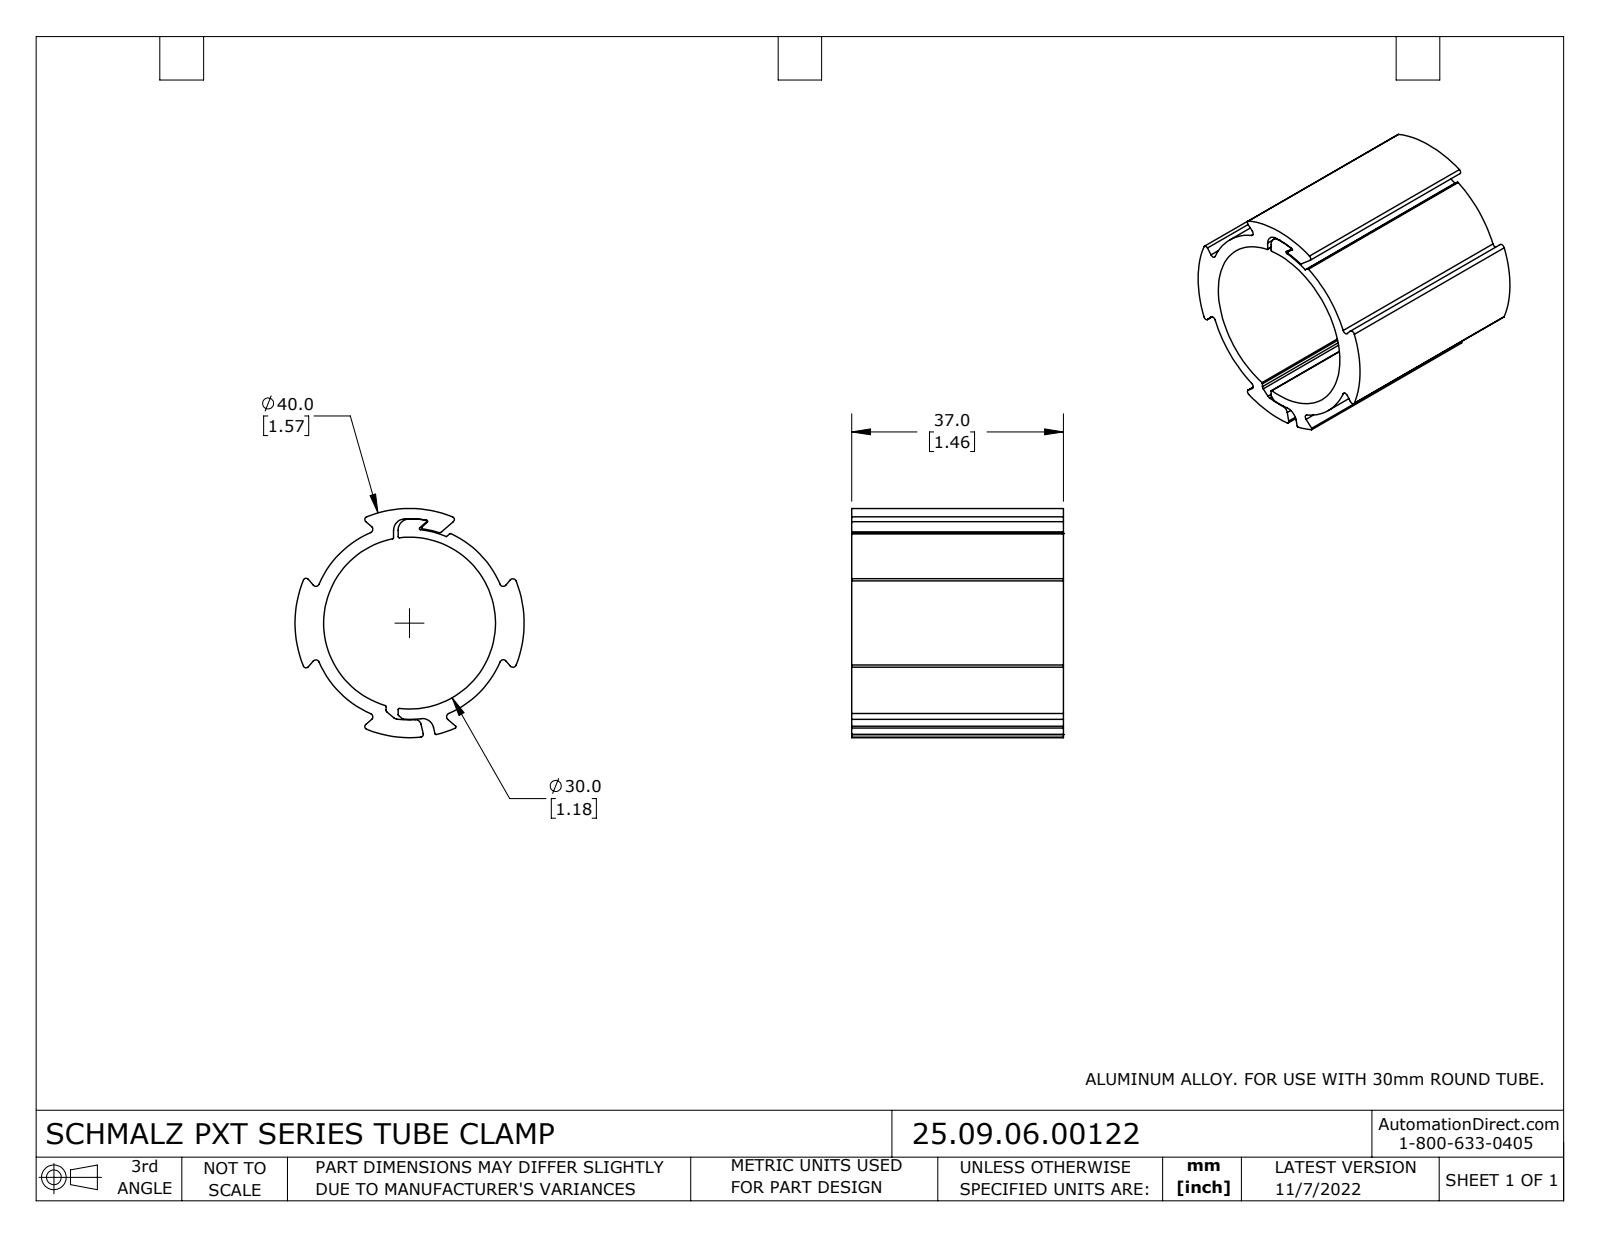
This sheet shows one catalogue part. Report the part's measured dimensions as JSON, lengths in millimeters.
{"part_name": "25.09.06.00122", "step_written_by": "SolidWorks 2021 (CONFIG_CONTROL_DESIGN)", "units": "millimeters", "bodies": {"solids": 2, "faces": 75, "planar": 23, "cylindrical": 52, "other": 0}, "overall_size": [40, 40, 37], "volume_mm3": 13716, "surface_area_mm2": 11109, "round_holes": [[30, 1]], "partial_cylinders_radius": [[0.2, 13], [0.6, 9], [0.5, 8], [2, 3], [1, 2], [16.4, 1], [16.6, 1], [16.8, 1]], "face_to_face_distances": [37, 3.03, 19.85, 16.82, 0.8, 2.89, 19.71, 16.83, 1.99, 0.84]}
